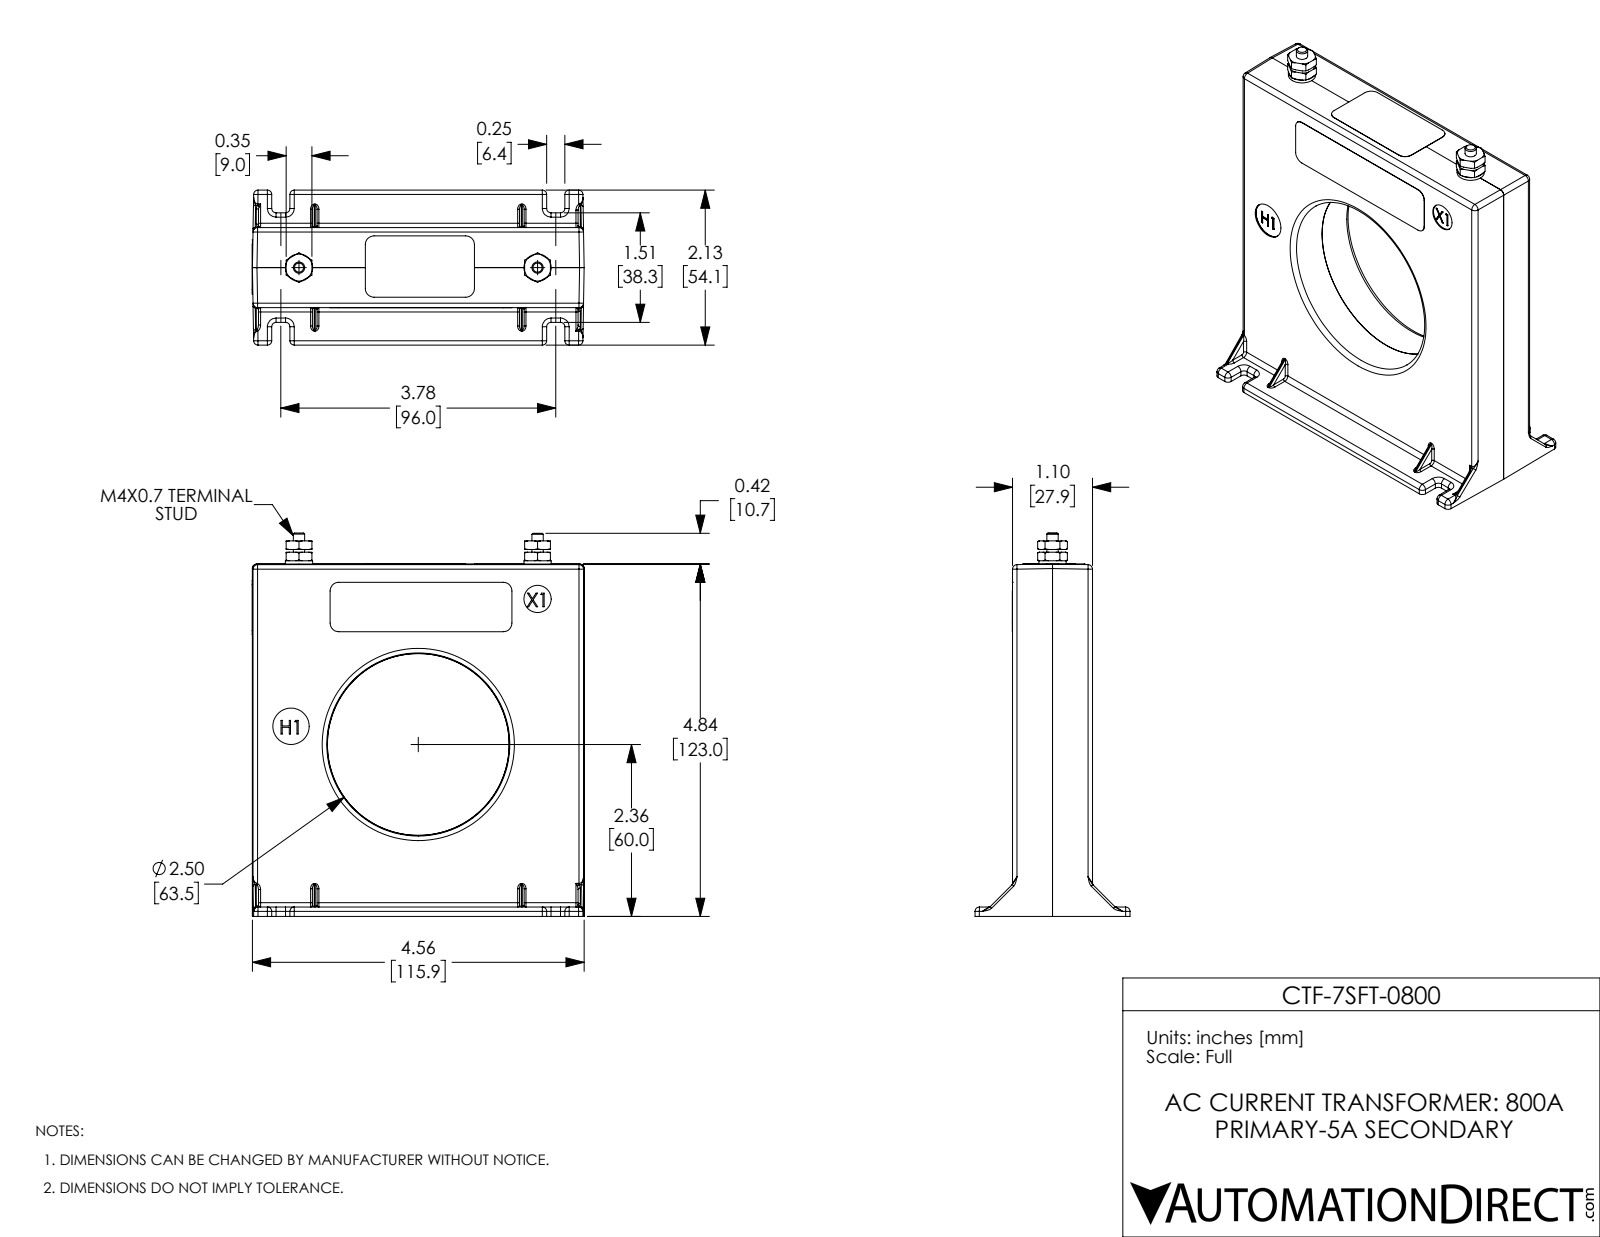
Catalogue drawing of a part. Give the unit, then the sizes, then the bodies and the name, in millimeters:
Units: millimetres
Overall size (bounding box): 133.9 × 117 × 54.1
Round holes (diameter × count): ⌀3.9 ×2, ⌀4.2 ×2, ⌀9.5 ×1, ⌀12.7 ×1
Round bosses / shafts (diameter × count): ⌀9.5 ×2
Partial cylindrical surfaces — rounded edges, fillets, slot ends (radius × count): R1.5 ×37, R0.6 ×25, R0.8 ×18, R1.6 ×5, R1.6 ×5, R3 ×5
Main face-to-face distances: 14, 27.9, 115.8, 3.3, 14, 28, 123, 119.7, 123.1, 119.8
Hole centre spacings: 83.3, 96.9
Volume: 318 100 mm³ · Surface area: 74 710 mm²
Bodies: 14 solids, 467 faces (172 planar, 143 cylindrical, 152 other)
Part name (STEP PRODUCT): CTF-7SFT-0800
STEP written by: SolidWorks 2018 (AUTOMOTIVE_DESIGN)
